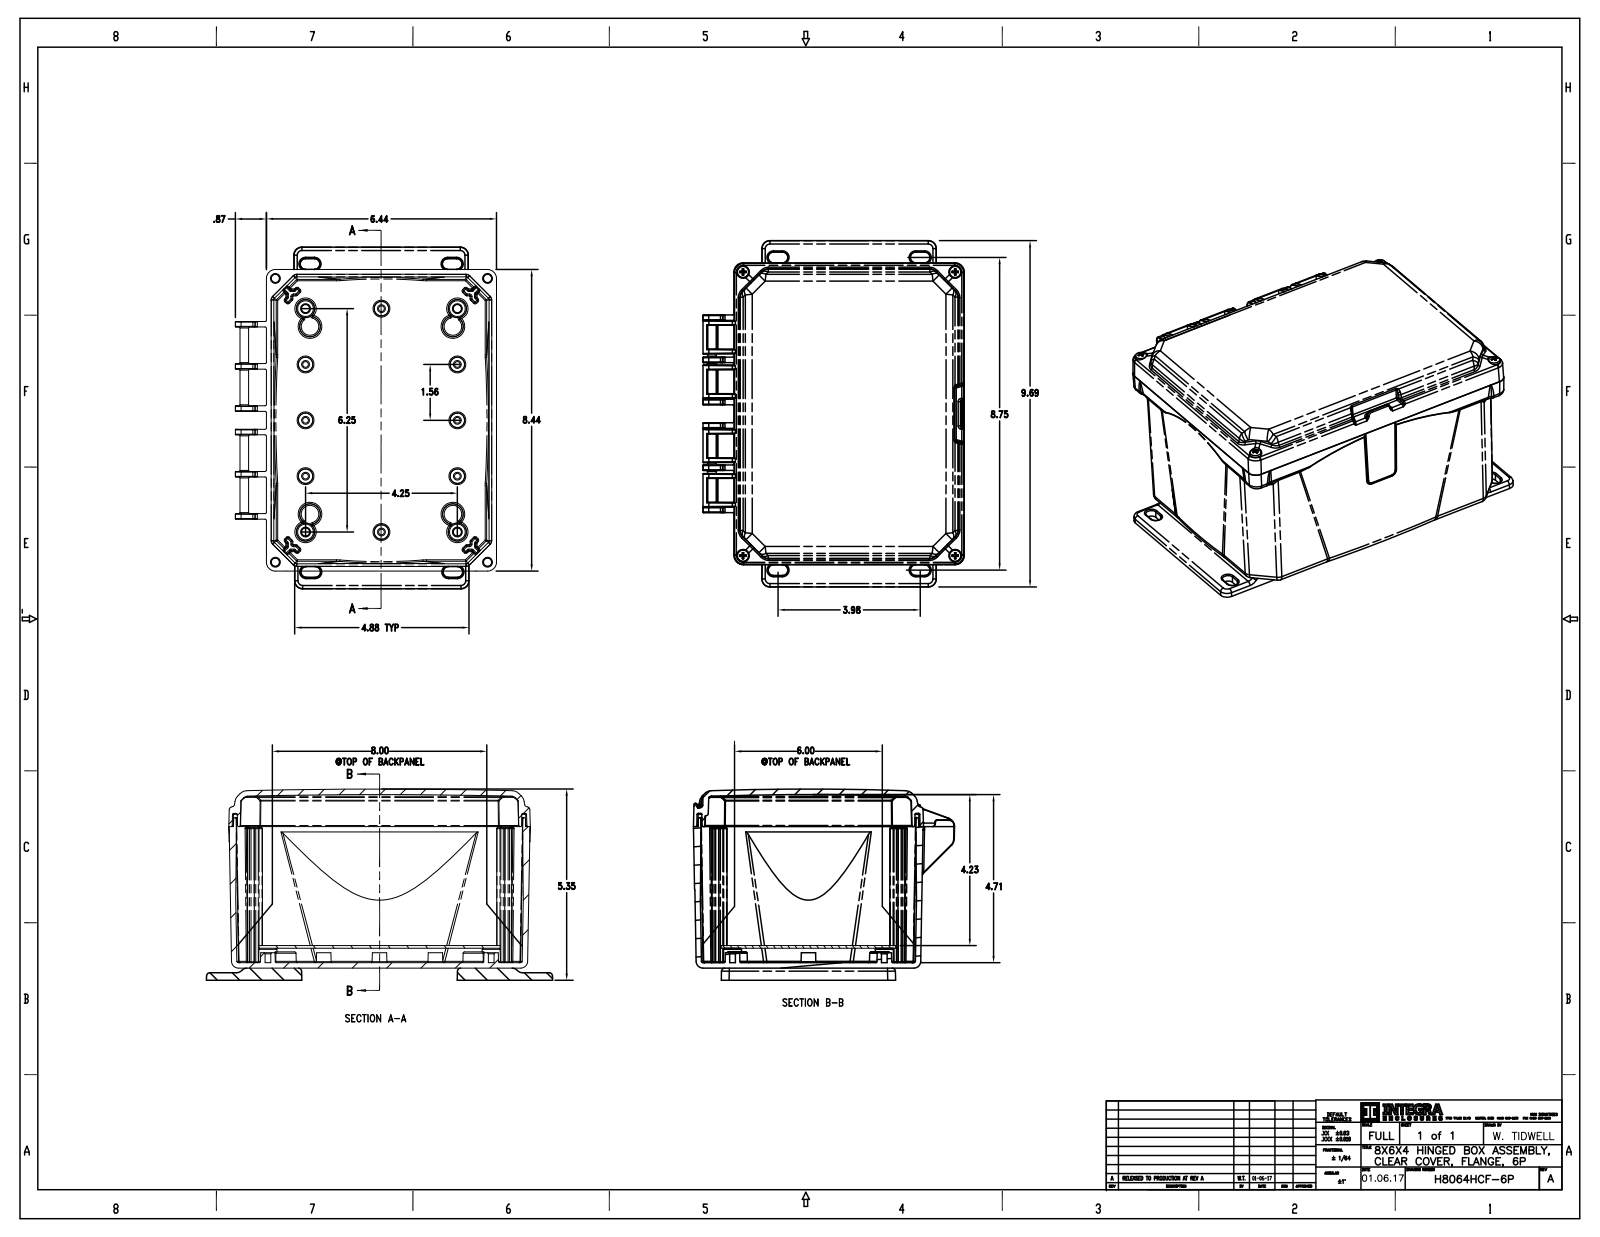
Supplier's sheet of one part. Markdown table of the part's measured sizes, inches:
| quantity | value |
| --- | --- |
| part name | H864BH; 9912525-80-10; 9912521-80-10; H864BH_ASM (+5 more) |
| STEP written by | CREO PARAMETRIC BY PTC INC, 2016050 (CONFIG_CONTROL_DESIGN) |
| units | inches |
| bodies | 24 solids, 3810 faces (875 planar, 1515 cylindrical, 1420 other) |
| overall size | 9.69 × 7.309 × 5.35 |
| volume | 44.81 in³ |
| surface area | 638.9 in² |
| round holes (diameter × count) | 0.16 × 8, 0.19 × 8, 0.201 × 4 |
| round bosses / shafts (diameter × count) | 0.25 × 12, 0.3 × 8, 0.298 × 8, 0.29 × 8, 0.26 × 8, 0.258 × 8, 0.375 × 4, 0.372 × 4 |
| partial cylindrical surfaces (radius × count) | 0.03 × 321, 0.025 × 64, 0.02 × 62, 0.015 × 60, 0.005 × 48, 0.09 × 44, 0.04 × 41, 0.06 × 39 |
| main face-to-face distances | 0.15, 0.32, 0.12, 0.34, 0.225, 0.49, 0.095, 3.96, 3.81, 0.22 |
| hole center spacings | 4.25, 0.516, 1.069, 1.195, 1.562, 1.563, 1.659, 2.062 |
